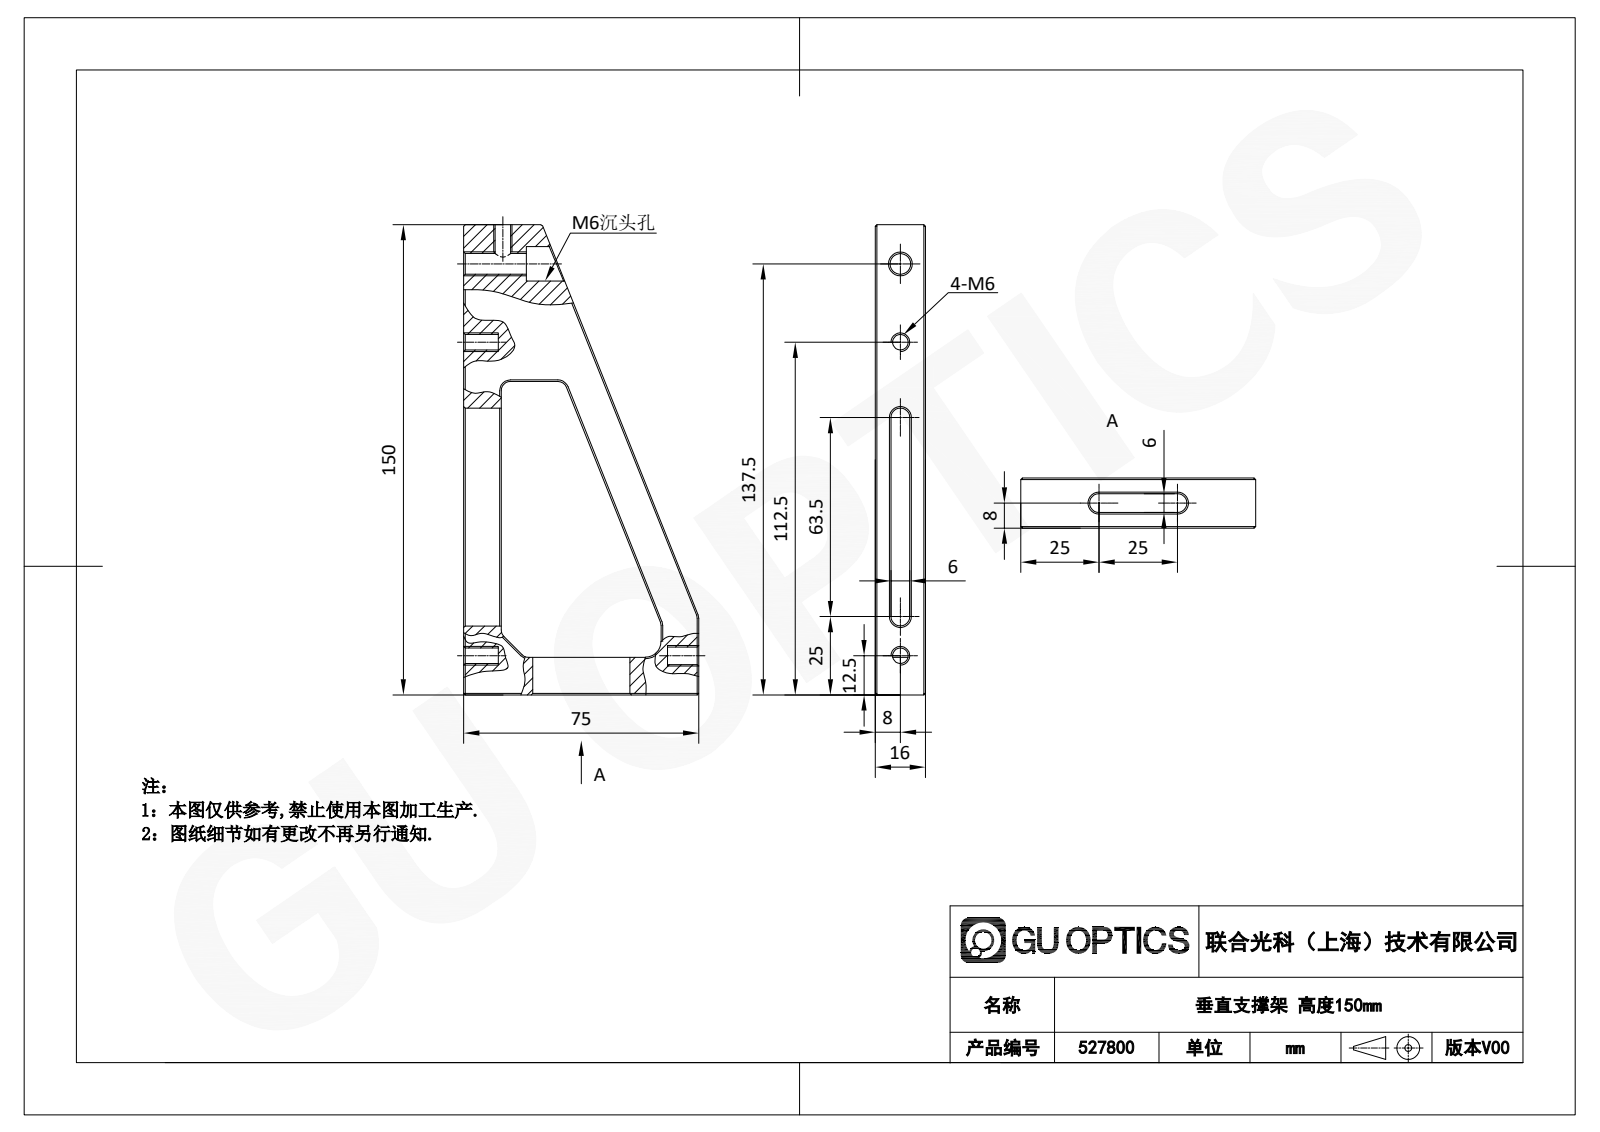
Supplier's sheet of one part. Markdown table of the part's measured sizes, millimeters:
| quantity | value |
| --- | --- |
| part name | 527800 |
| STEP written by | SolidWorks 2020 (CONFIG_CONTROL_DESIGN) |
| units | millimeters |
| bodies | 0 solids, 95 faces (43 planar, 21 cylindrical, 31 other) |
| overall size | 150 × 75 × 16 |
| round holes (diameter × count) | 5 × 3, 5.6 × 1, 6.6 × 1, 11 × 1 |
| partial cylindrical surfaces (radius × count) | 3 × 10, 0.5 × 4, 5 × 1 |
| main face-to-face distances | 16, 5, 11, 11.97, 12, 6, 63, 138, 150, 75 |
| hole center spacings | 25, 100, 125 |
